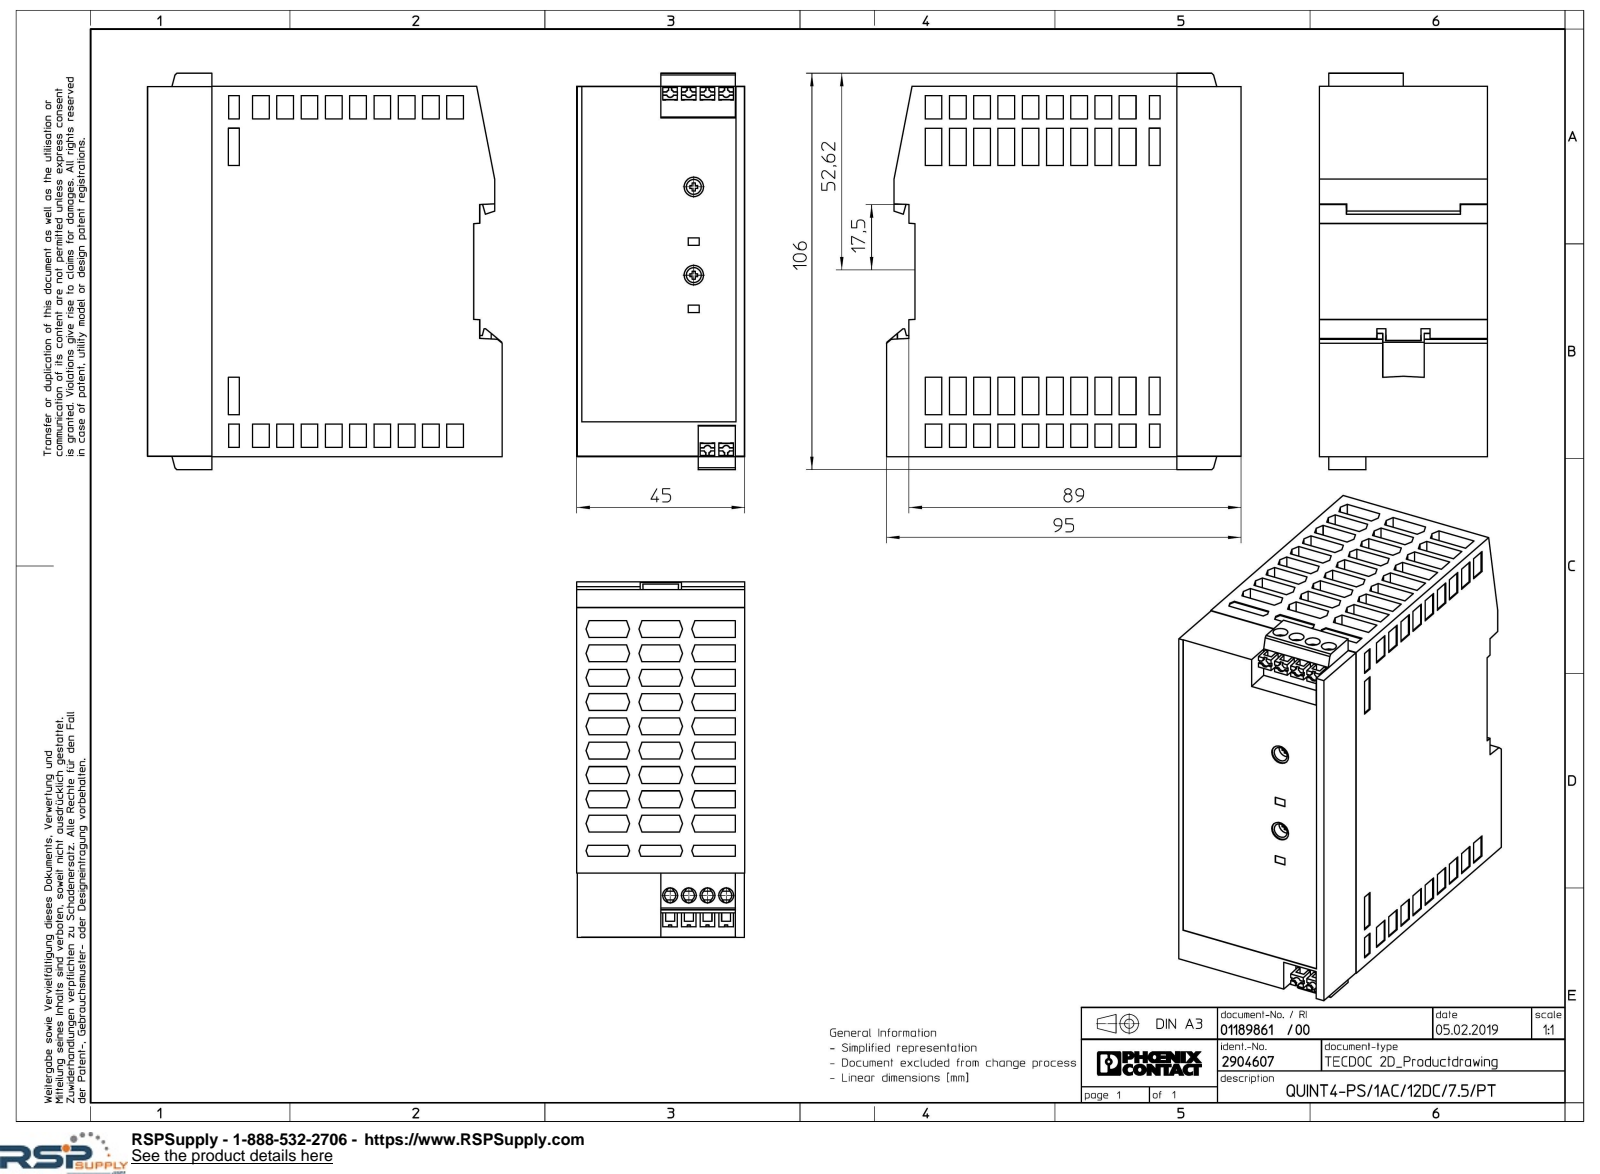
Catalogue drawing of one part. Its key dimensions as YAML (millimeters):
part_name: "QUINT4_PS_1AC_12DC_7.5_PT-select"
step_written_by: "Creo Elements/Direct Modeling 20.1A 29-Sep-2018 (C) Parametric Technology GmbH (AUTOMOTIVE_DESIGN)"
units: millimeters
bodies: {solids: 1, faces: 1035, planar: 973, cylindrical: 32, other: 30}
overall_size: [106, 95, 45]
volume: 396099
surface_area: 42702
round_holes:
  - {diameter: 4, count: 8}
  - {diameter: 5.2, count: 2}
partial_cylinders:
  - {radius: 1.5, count: 6}
face_to_face_distances: [45, 44.9, 3, 96, 6.5, 44.73, 44.63, 99, 44.8, 93]
hole_center_spacings: [5, 5.01, 10, 10.01, 4.99, 15, 15.01, 23.6]
